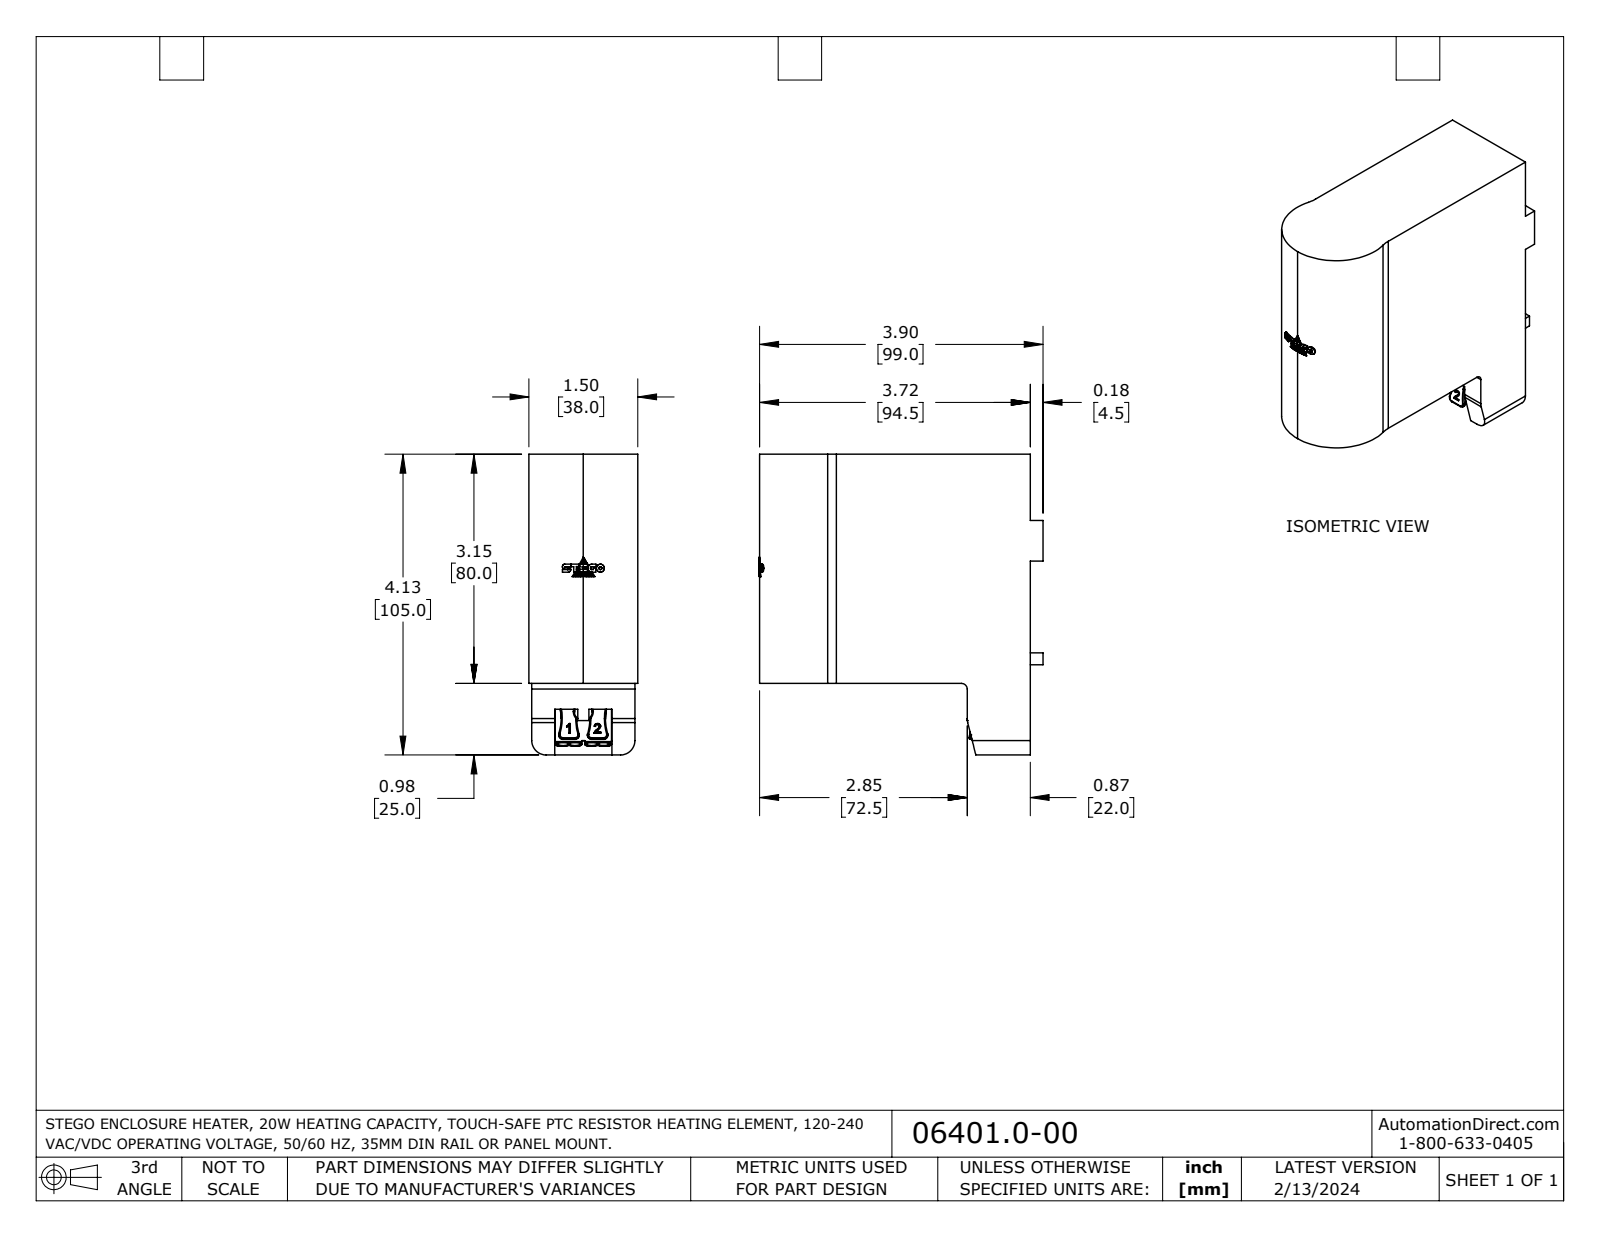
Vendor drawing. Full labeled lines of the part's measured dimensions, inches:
Part name (STEP PRODUCT): STEP_LTS064_1
STEP written by: SolidWorks 2022 (AUTOMOTIVE_DESIGN)
Units: inches
Bodies: 1 solid, 428 faces (216 planar, 102 cylindrical, 110 other)
Overall size (bounding box): 4.134 × 3.909 × 1.496
Volume: 16.8 in³ · Surface area: 53.98 in²
Partial cylindrical surfaces — rounded edges, fillets, slot ends (radius × count): R0.016 ×11, R0.012 ×6, R0.079 ×5, R0.028 ×4, R0.059 ×4, R0.738 ×4, R0.197 ×2, R0.472 ×2
Main face-to-face distances: 1.417, 3.15, 0.098, 0.846, 0.315, 1.319, 0.059, 0.787, 0.768, 1.102
